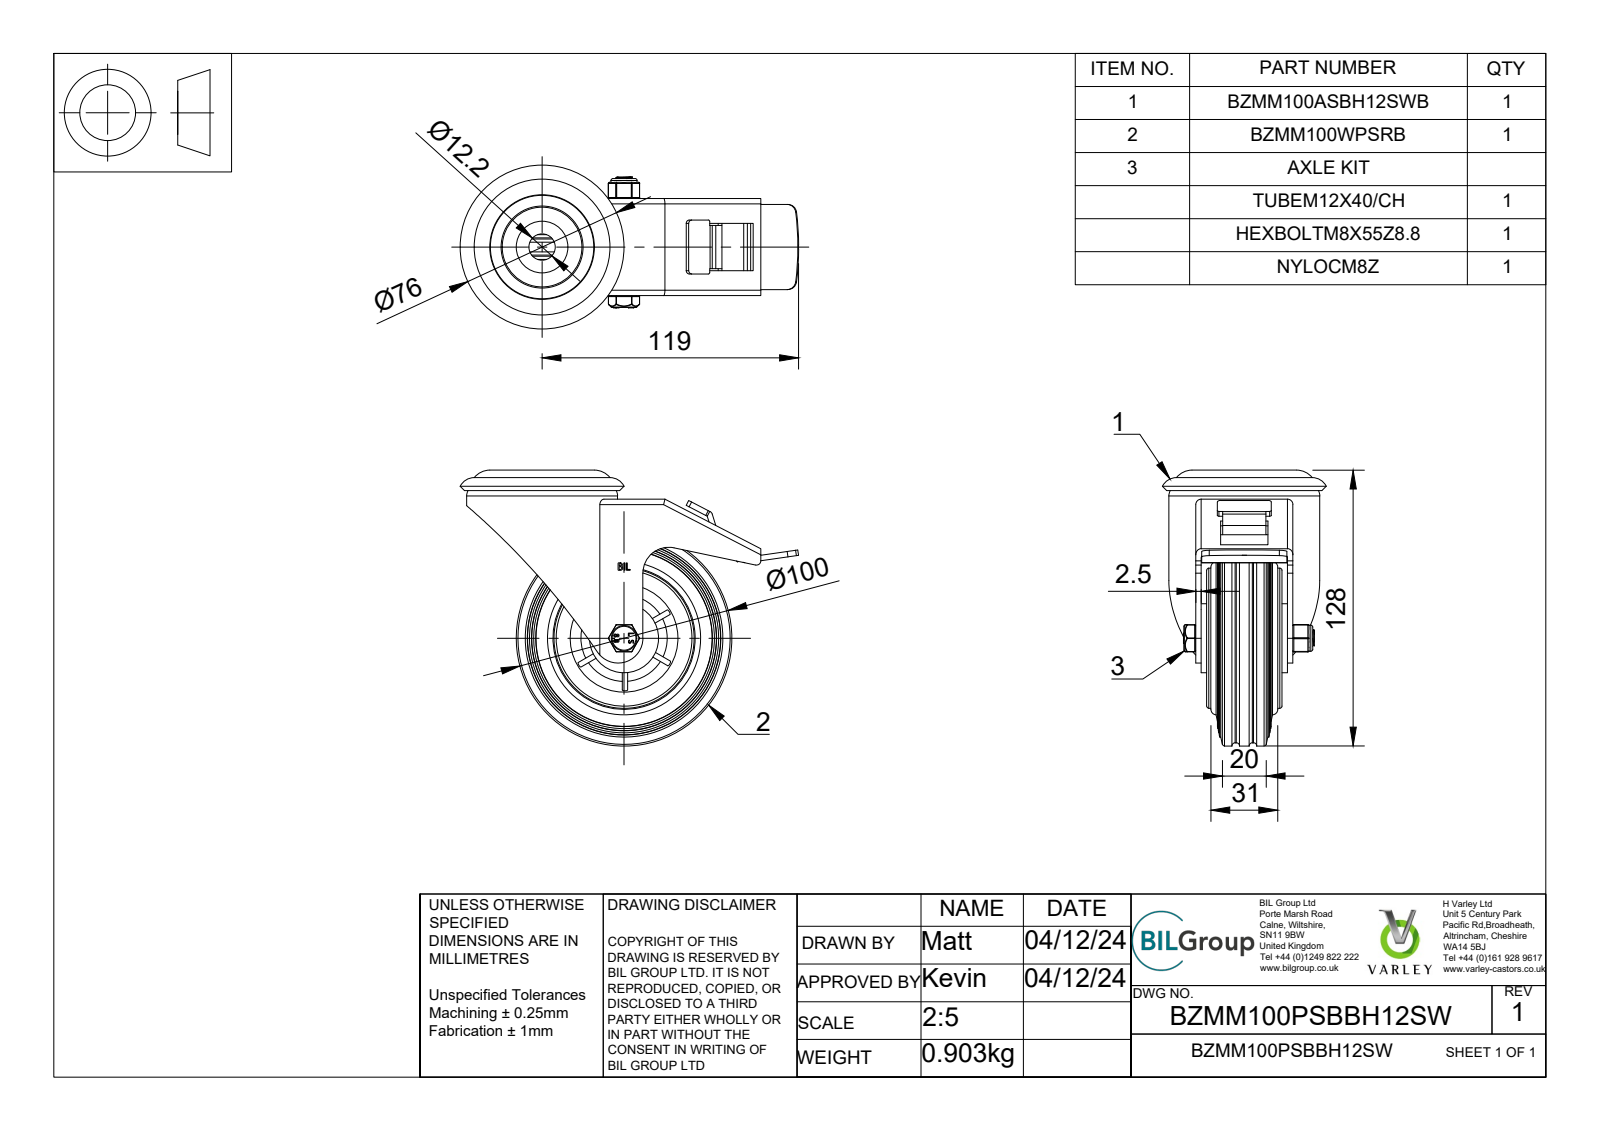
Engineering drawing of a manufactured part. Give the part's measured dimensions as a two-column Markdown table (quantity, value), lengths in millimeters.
| quantity | value |
| --- | --- |
| part name | BZMM100PSBBH12SW v3; BZMM100ASBH12SWB v1; PRESSED STEEL, ZINC PLATED HEAD; PRESSED STEEL, ZINC PLATED FORKS (+7 more) |
| STEP written by | Autodesk Translation Framework v13.20.0.188 (AP242_MANAGED_MODEL_BASED_3D_ENGINEERING_MIM_LF) |
| units | millimeters |
| bodies | 20 solids, 757 faces (379 planar, 245 cylindrical, 133 other) |
| overall size | 157 × 128 × 76 |
| volume | 274 476 mm³ |
| surface area | 126 808 mm² |
| round holes (diameter × count) | 0.66 × 2, 8 × 1, 8.2 × 1, 8.4 × 1, 8.6 × 1, 12.2 × 1, 12.5 × 1, 15 × 1, 15.5 × 1, 21 × 1, 27 × 1, 65 × 1 |
| round bosses / shafts (diameter × count) | 3.75 × 8, 100 × 1, 97 × 1, 70 × 1, 65 × 1, 49.5 × 1, 38 × 1, 32 × 1 |
| partial cylindrical surfaces (radius × count) | 0.75 × 50, 1.25 × 22, 0.5 × 18, 0.25 × 12, 0.33 × 4, 0.64 × 4, 2.5 × 4, 2 × 3 |
| main face-to-face distances | 2.5, 4.5, 7, 35.5, 40, 38, 42.5, 2, 31, 5 |
| hole center spacings | 3.22, 2.49 |
